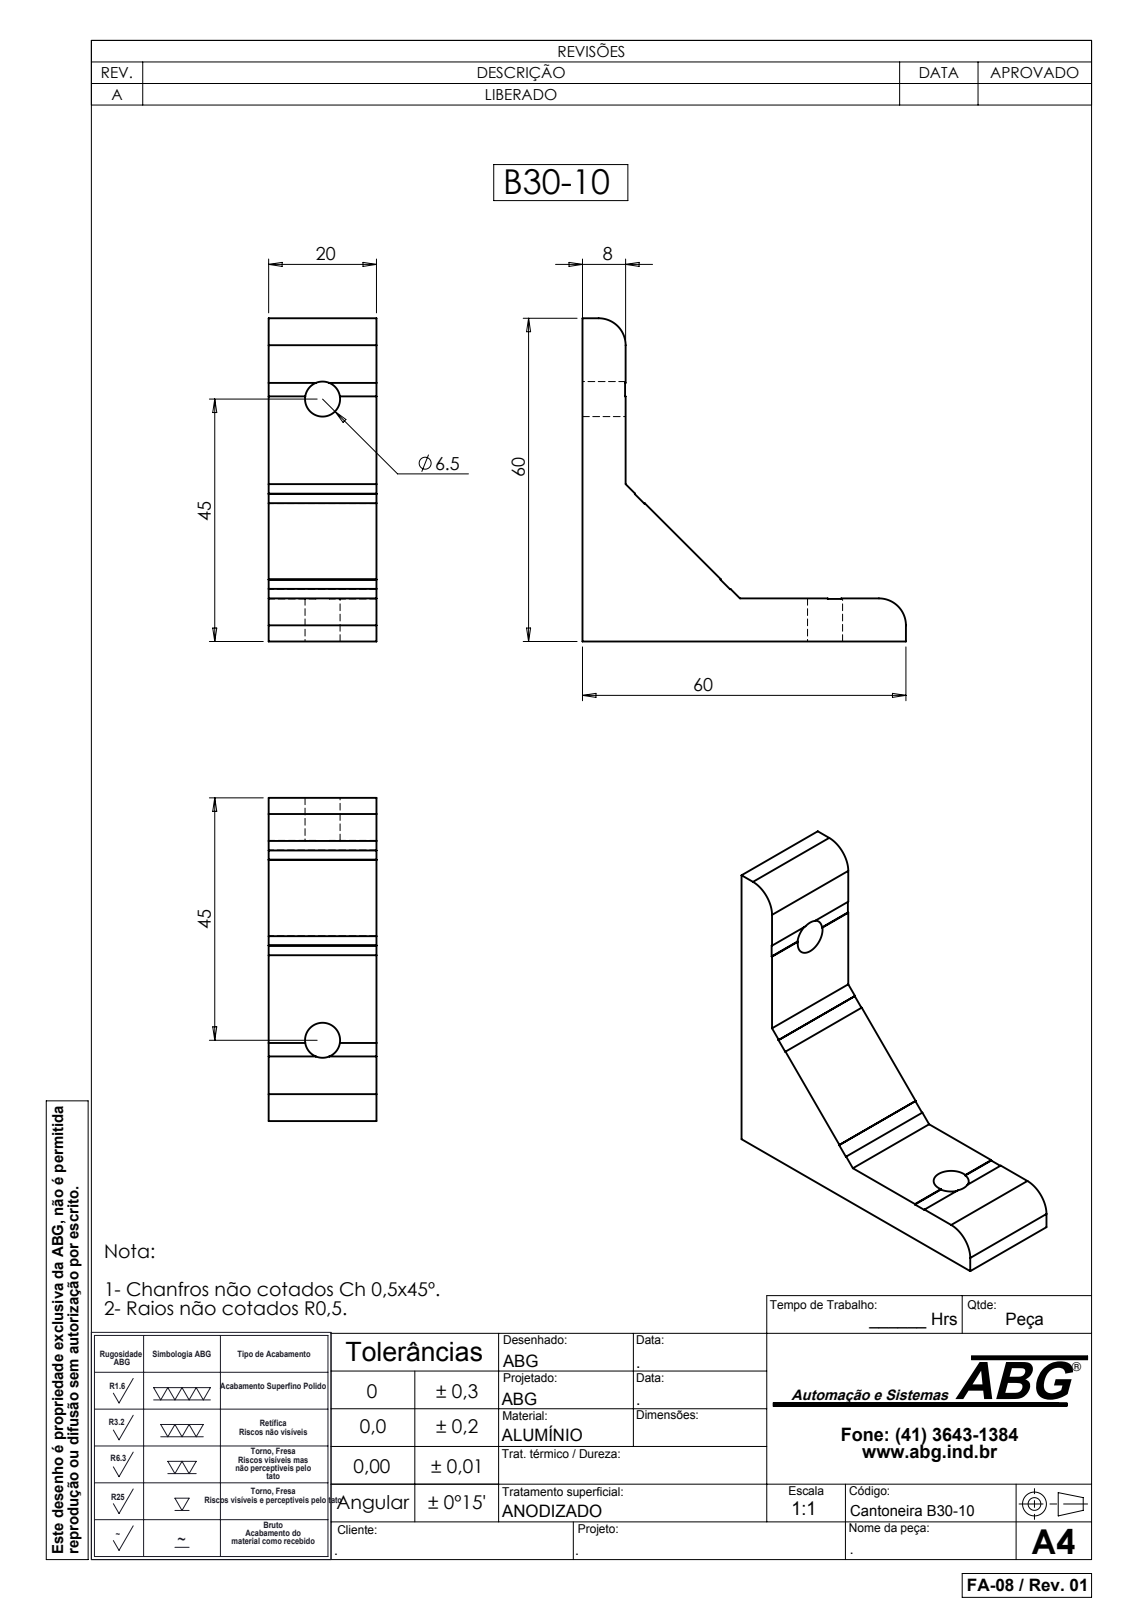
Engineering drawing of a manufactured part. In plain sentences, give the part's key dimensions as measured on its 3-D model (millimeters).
The part is named "B30-10". Its 3-D file was written by "SolidWorks 2007 (CONFIG_CONTROL_DESIGN)". It is 1 solid with 37 faces: 31 planar, 6 cylindrical and 0 other. Overall it measures 60 by 60 by 20 millimeters. Its volume is 21 657 cubic millimeters and its surface area 6 891 square millimeters. Round holes: 2 of diameter 6.5. Partial cylindrical surfaces (rounded edges, fillets, slot ends): 2 of radius 5. The main face-to-face distances are 20, 8, 52, 60, 52.1, 7.9, 2.5, 22.5, 12, 40.
